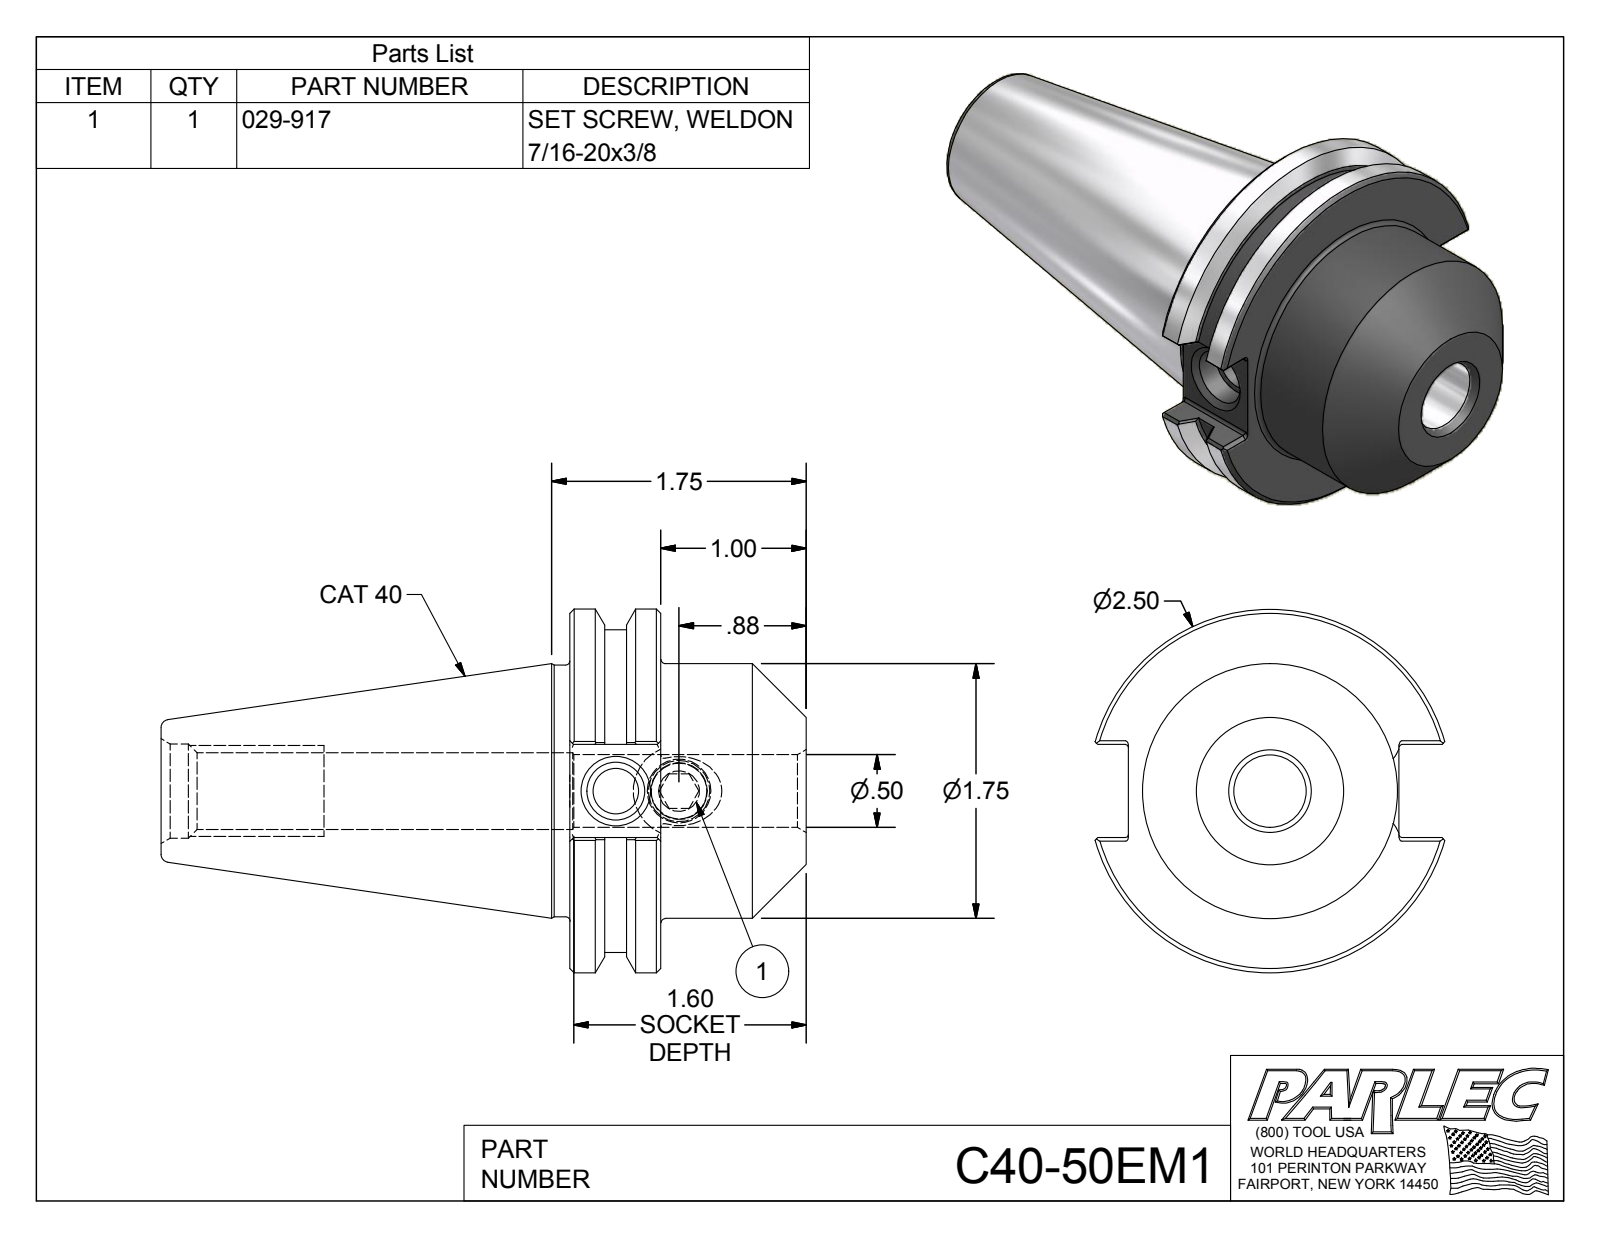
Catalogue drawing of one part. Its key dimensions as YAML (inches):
part_name: "C40-50EM1; C40-50EM1-1; 029-917"
step_written_by: "Autodesk Inventor 2012 (AUTOMOTIVE_DESIGN)"
units: inches
bodies: {solids: 2, faces: 98, planar: 40, cylindrical: 27, other: 31}
overall_size: [4.437, 2.5, 2.406]
volume: 7.981
surface_area: 38.35
round_holes:
  - {diameter: 0.315, count: 1}
  - {diameter: 0.383, count: 1}
  - {diameter: 0.399, count: 1}
  - {diameter: 0.5, count: 1}
  - {diameter: 0.527, count: 1}
  - {diameter: 0.648, count: 1}
round_bosses_or_shafts:
  - {diameter: 2.5, count: 1}
  - {diameter: 2.219, count: 1}
  - {diameter: 1.75, count: 1}
  - {diameter: 1.73, count: 1}
  - {diameter: 0.437, count: 1}
partial_cylinders:
  - {radius: 0.02, count: 12}
face_to_face_distances: [0.625, 1.625, 1, 0.236, 0.64, 1.86, 2.812, 3.437, 4.437, 3.201]
hole_center_spacings: [0.435]
